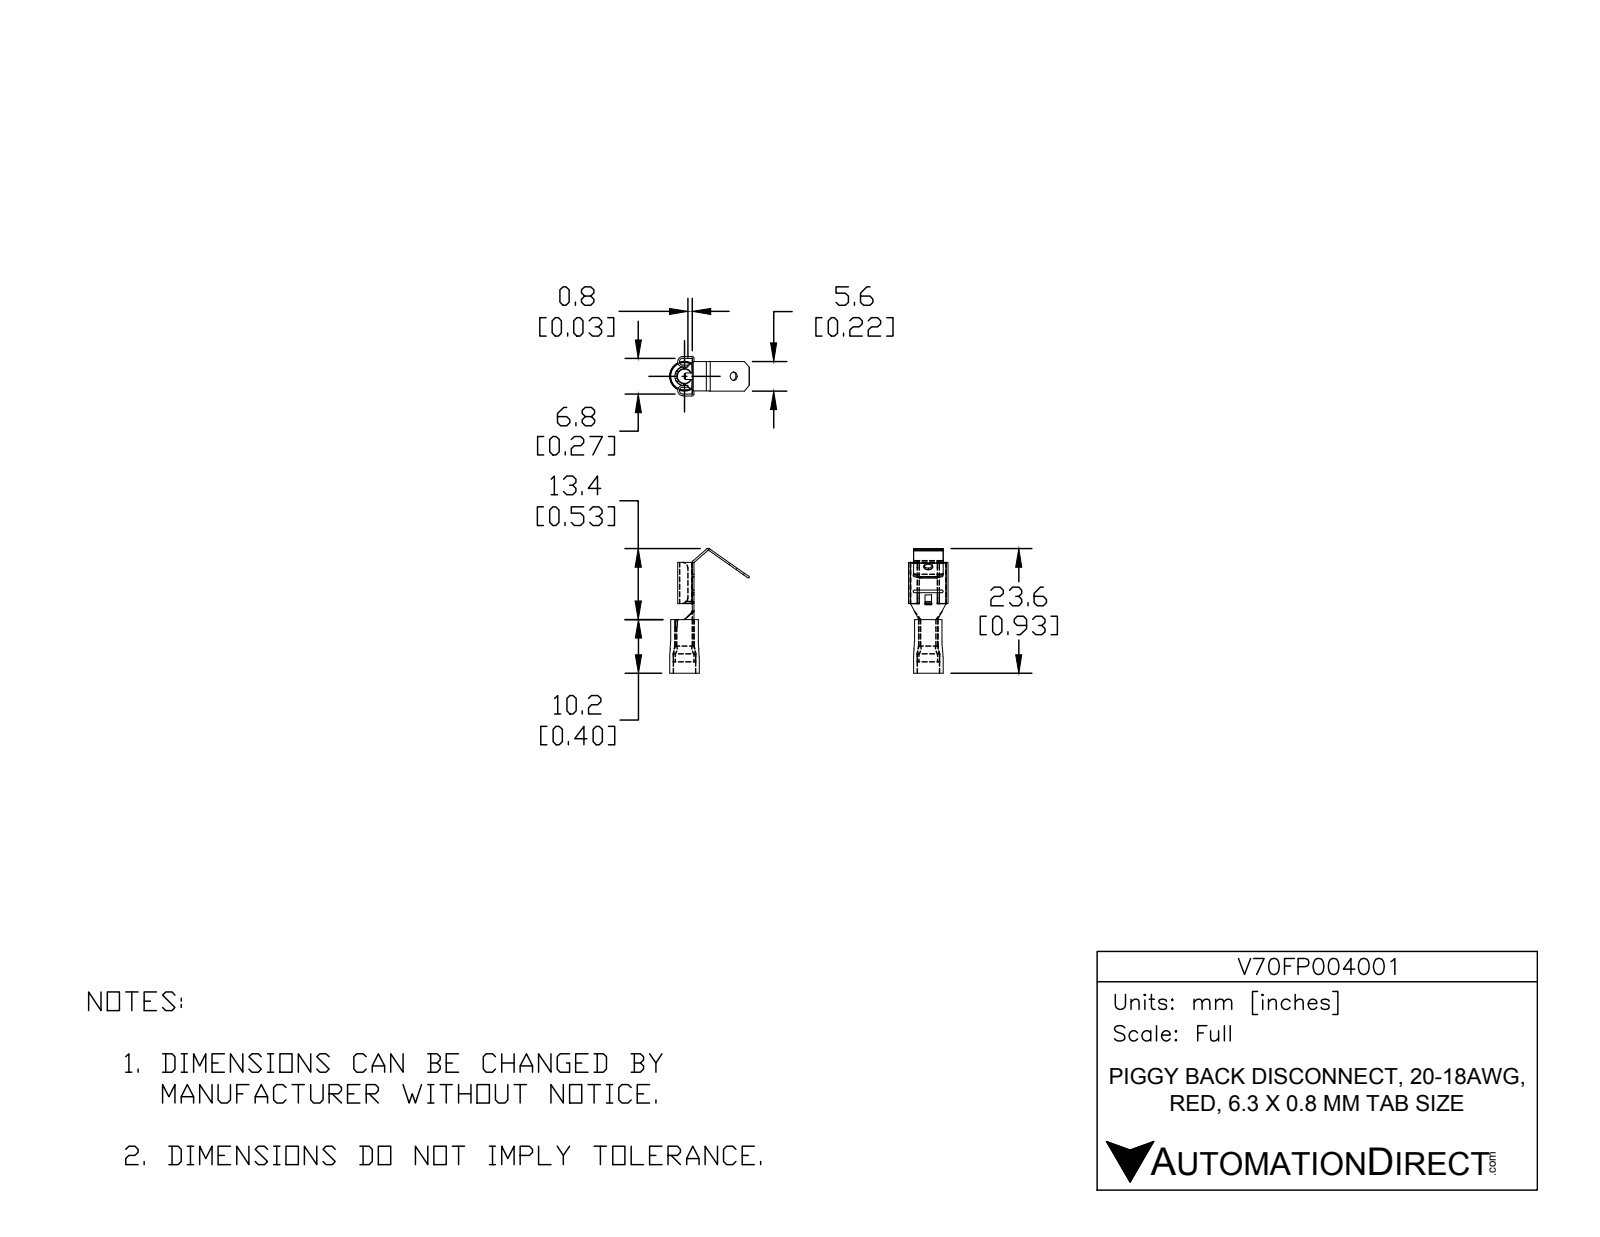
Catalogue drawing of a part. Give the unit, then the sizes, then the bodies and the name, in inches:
Units: inches
Overall size (bounding box): 0.929 × 0.593 × 0.294
Round holes (diameter × count): ⌀0.063 ×1, ⌀0.114 ×1, ⌀0.139 ×1, ⌀0.142 ×1, ⌀0.167 ×1
Round bosses / shafts (diameter × count): ⌀0.22 ×1, ⌀0.205 ×1
Partial cylindrical surfaces — rounded edges, fillets, slot ends (radius × count): R0.01 ×8, R0.02 ×4, R0.039 ×4, R0.015 ×2, R0.024 ×2, R0.026 ×2
Main face-to-face distances: 0.014, 0.065, 0.215, 0.28, 0.079, 0.229, 0.051, 0.201, 0.15, 0.266
Volume: 0.013 in³ · Surface area: 1.51 in²
Bodies: 2 solids, 123 faces (49 planar, 50 cylindrical, 24 other)
Part name (STEP PRODUCT): V70FP004001
STEP written by: SolidWorks 2017 (AUTOMOTIVE_DESIGN)
